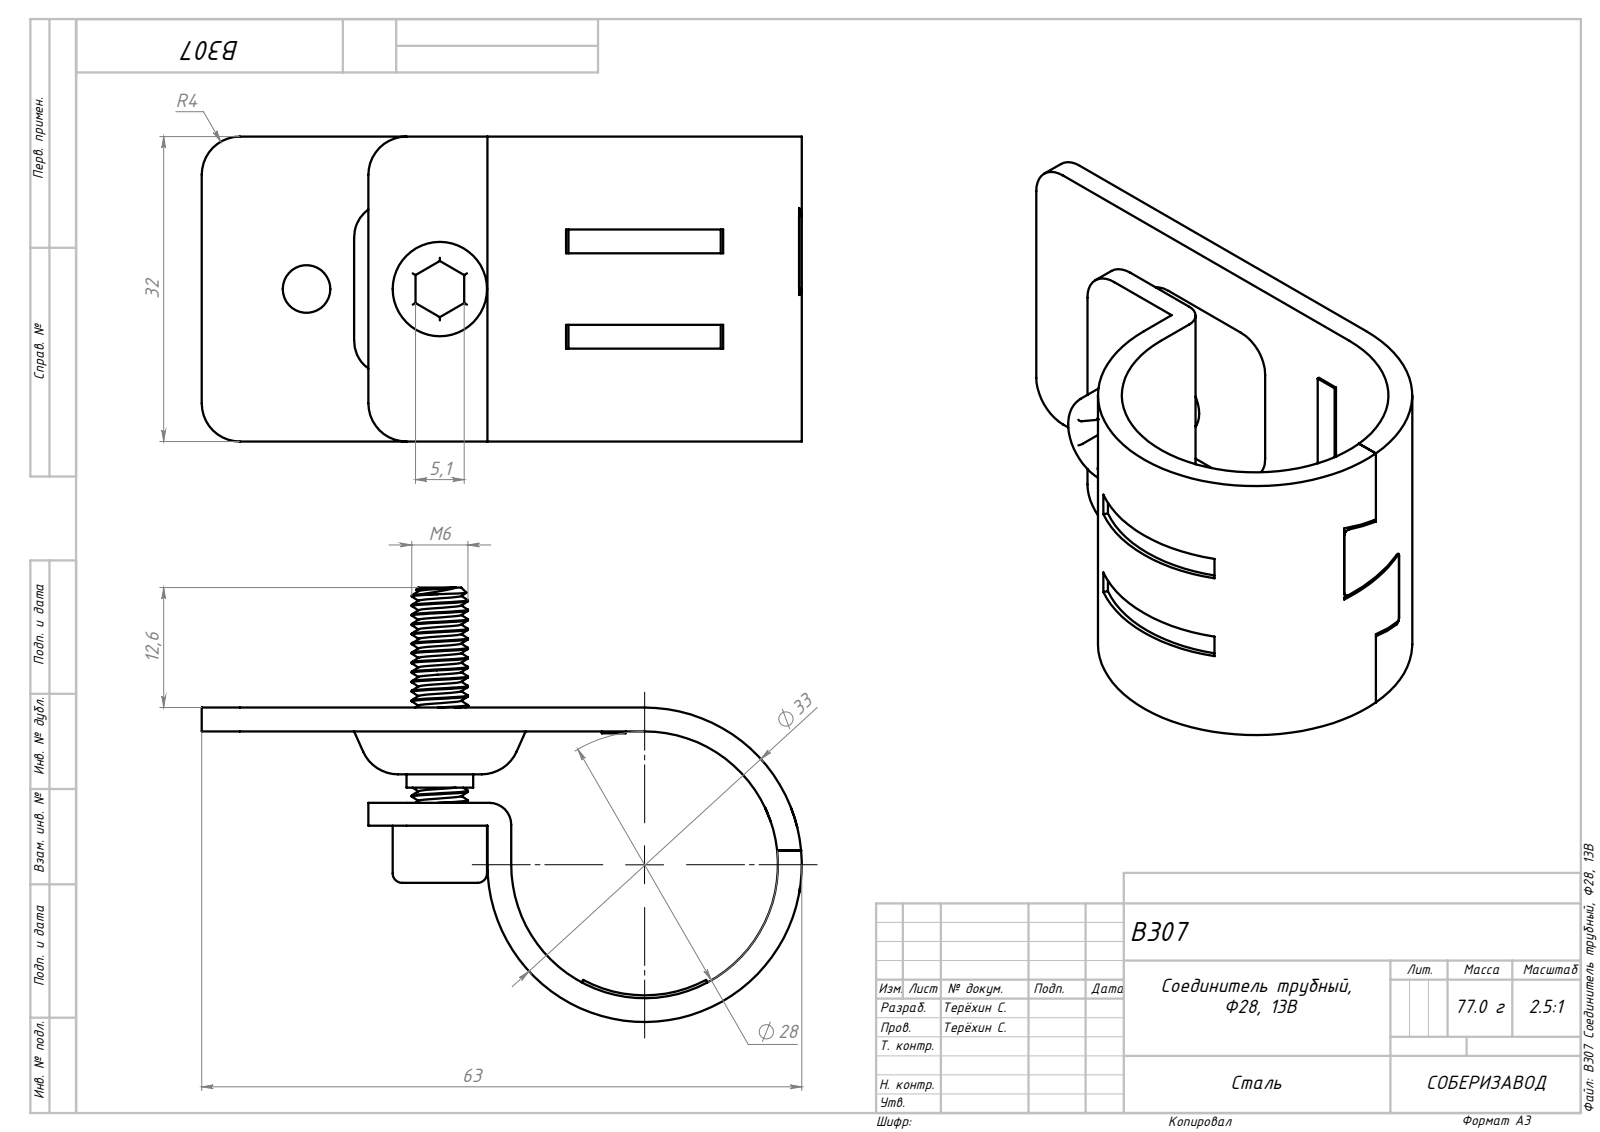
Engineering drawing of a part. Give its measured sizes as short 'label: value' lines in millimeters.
name: B307 Соединитель трубный, Ф28, 13B
written by: SolidWorks 2022 (AUTOMOTIVE_DESIGN)
unit: mm
bodies: 4 solids, 232 faces (86 planar, 113 cylindrical, 33 other)
size: 63 × 45.6 × 32
volume: 12 103 mm³; area: 11 655 mm²
holes: 1× ⌀5, 1× ⌀5.3, 1× ⌀7, 1× ⌀7.4
bosses: 1× ⌀9.9, 1× ⌀5.9
rounds: 16× R4, 6× R0.3, 4× R0.5, 4× R3, 1× R2.3, 1× R13.7, 1× R14, 1× R16
face distances: 2.5, 10, 9.9, 12.4, 7.5, 2.4, 32, 4.5, 12.5, 15
hole spacings: 14
